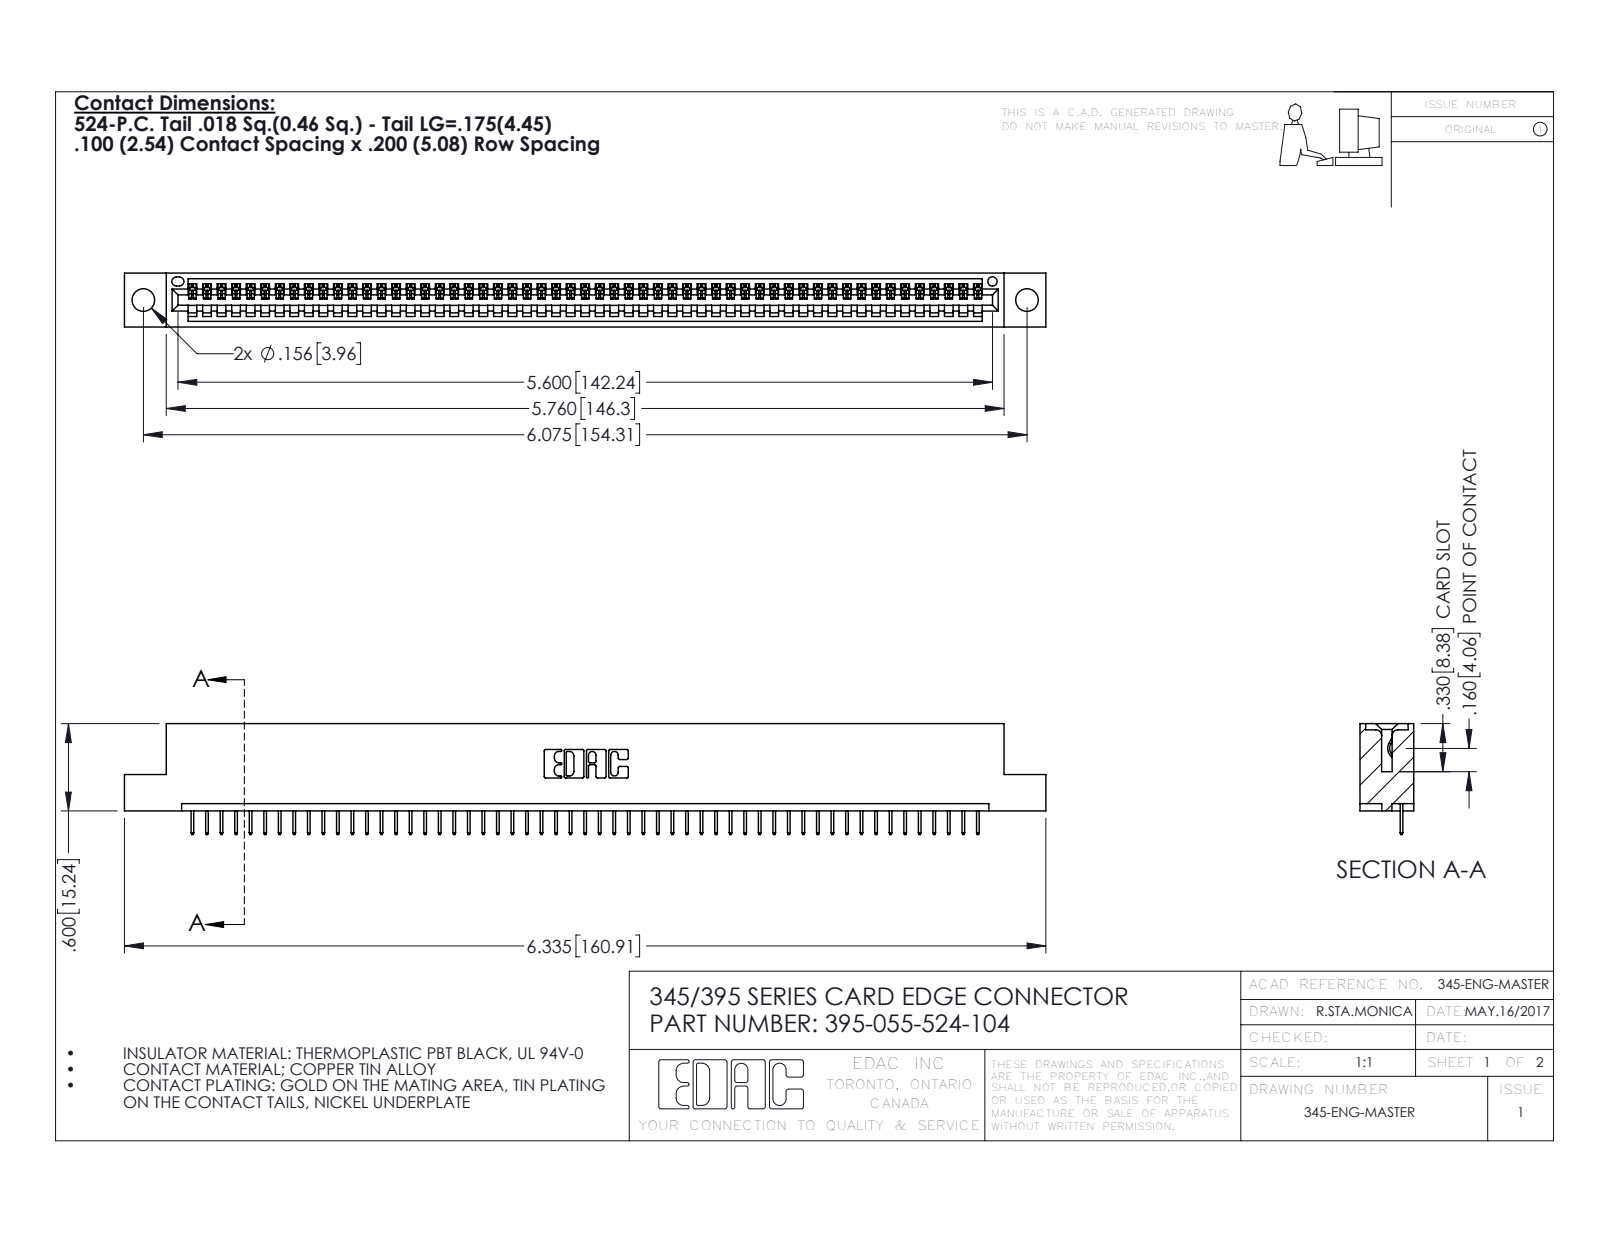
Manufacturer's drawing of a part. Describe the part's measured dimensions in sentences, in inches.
The part is named "345 Part_Flush Mounting Lugs - 0.156 Dia-TH; 395-055-524-104; 345-292-001_345-293-124". Its 3-D file was written by "SolidWorks 2016 (CONFIG_CONTROL_DESIGN)". It is 56 solids with 3536 faces: 2610 planar, 926 cylindrical and 0 other. Overall it measures 6.335 by 0.762 by 0.37 inches. Its volume is 0.921 cubic inches and its surface area 29.97 square inches. Round holes: 2 of diameter 0.156, 1 of diameter 0.064. Partial cylindrical surfaces (rounded edges, fillets, slot ends): 110 of radius 0.006, 22 of radius 0.01, 6 of radius 0.007, 6 of radius 0.031, 3 of radius 0.026, 2 of radius 0.031, 2 of radius 0.04, 1 of radius 0.014. The main face-to-face distances are 0.072, 0.298, 0.37, 0.2, 0.098, 0.272, 0.025, 0.225, 0.072, 0.149. The hole center spacings are 0.27, 5.839, 6.075.
